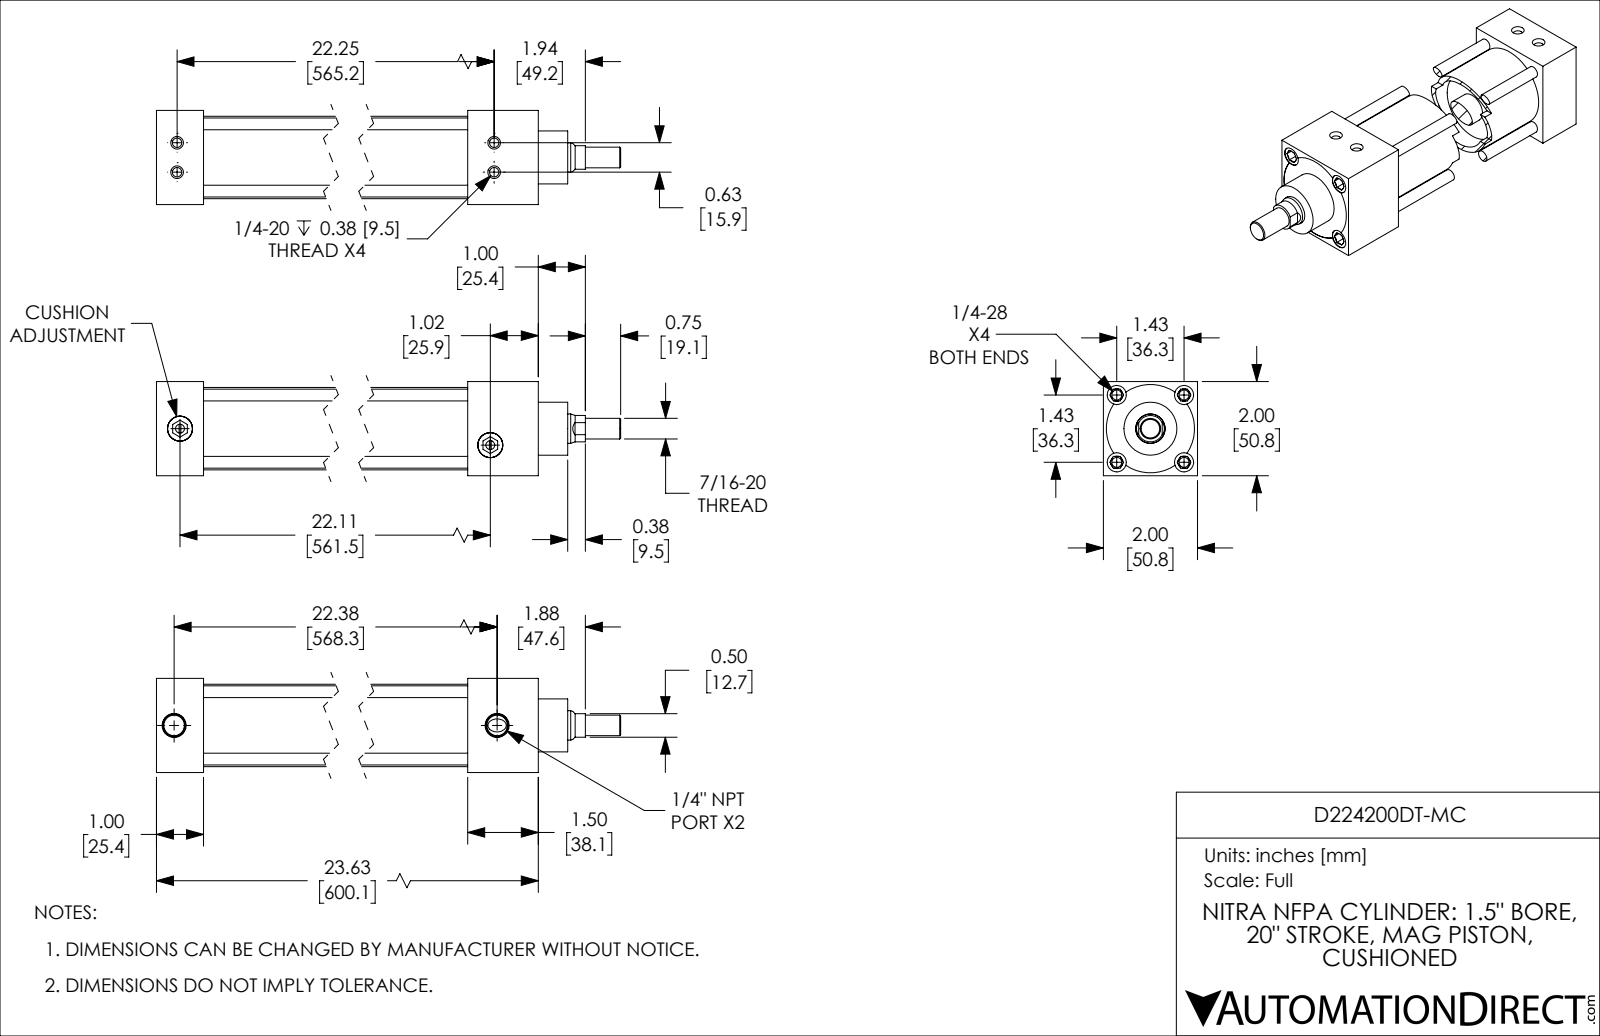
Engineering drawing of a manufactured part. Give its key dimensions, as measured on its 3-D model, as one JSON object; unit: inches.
{"part_name": "D224200DT-MC_PISTON_KK1; D224200DT-MC_CUSHION; D224200DT-MC; D224200DT-MC_BODY", "step_written_by": "SolidWorks 2019 (CONFIG_CONTROL_DESIGN)", "units": "inches", "bodies": {"solids": 4, "faces": 251, "planar": 90, "cylindrical": 81, "other": 80}, "overall_size": [25.375, 2, 2], "volume_in3": 35.99, "surface_area_in2": 385.2, "round_holes": [[0.201, 4], [0.213, 4], [0.406, 4], [0.19, 2], [0.438, 2], [0.531, 2], [0.626, 1], [1.501, 1]], "round_bosses_or_shafts": [[0.25, 4], [0.532, 2], [1.751, 1], [1.499, 1], [1.125, 1], [0.624, 1], [0.437, 1]], "partial_cylinders_radius": [[0.281, 1], [0.937, 1]], "face_to_face_distances": [2, 1, 22.125, 21.125, 2.125, 23.62, 22.62, 1.495, 1.125, 20], "hole_center_spacings": [0.319, 1.011, 1.43, 0.625, 2.022, 22.25, 22.259, 22.315]}
